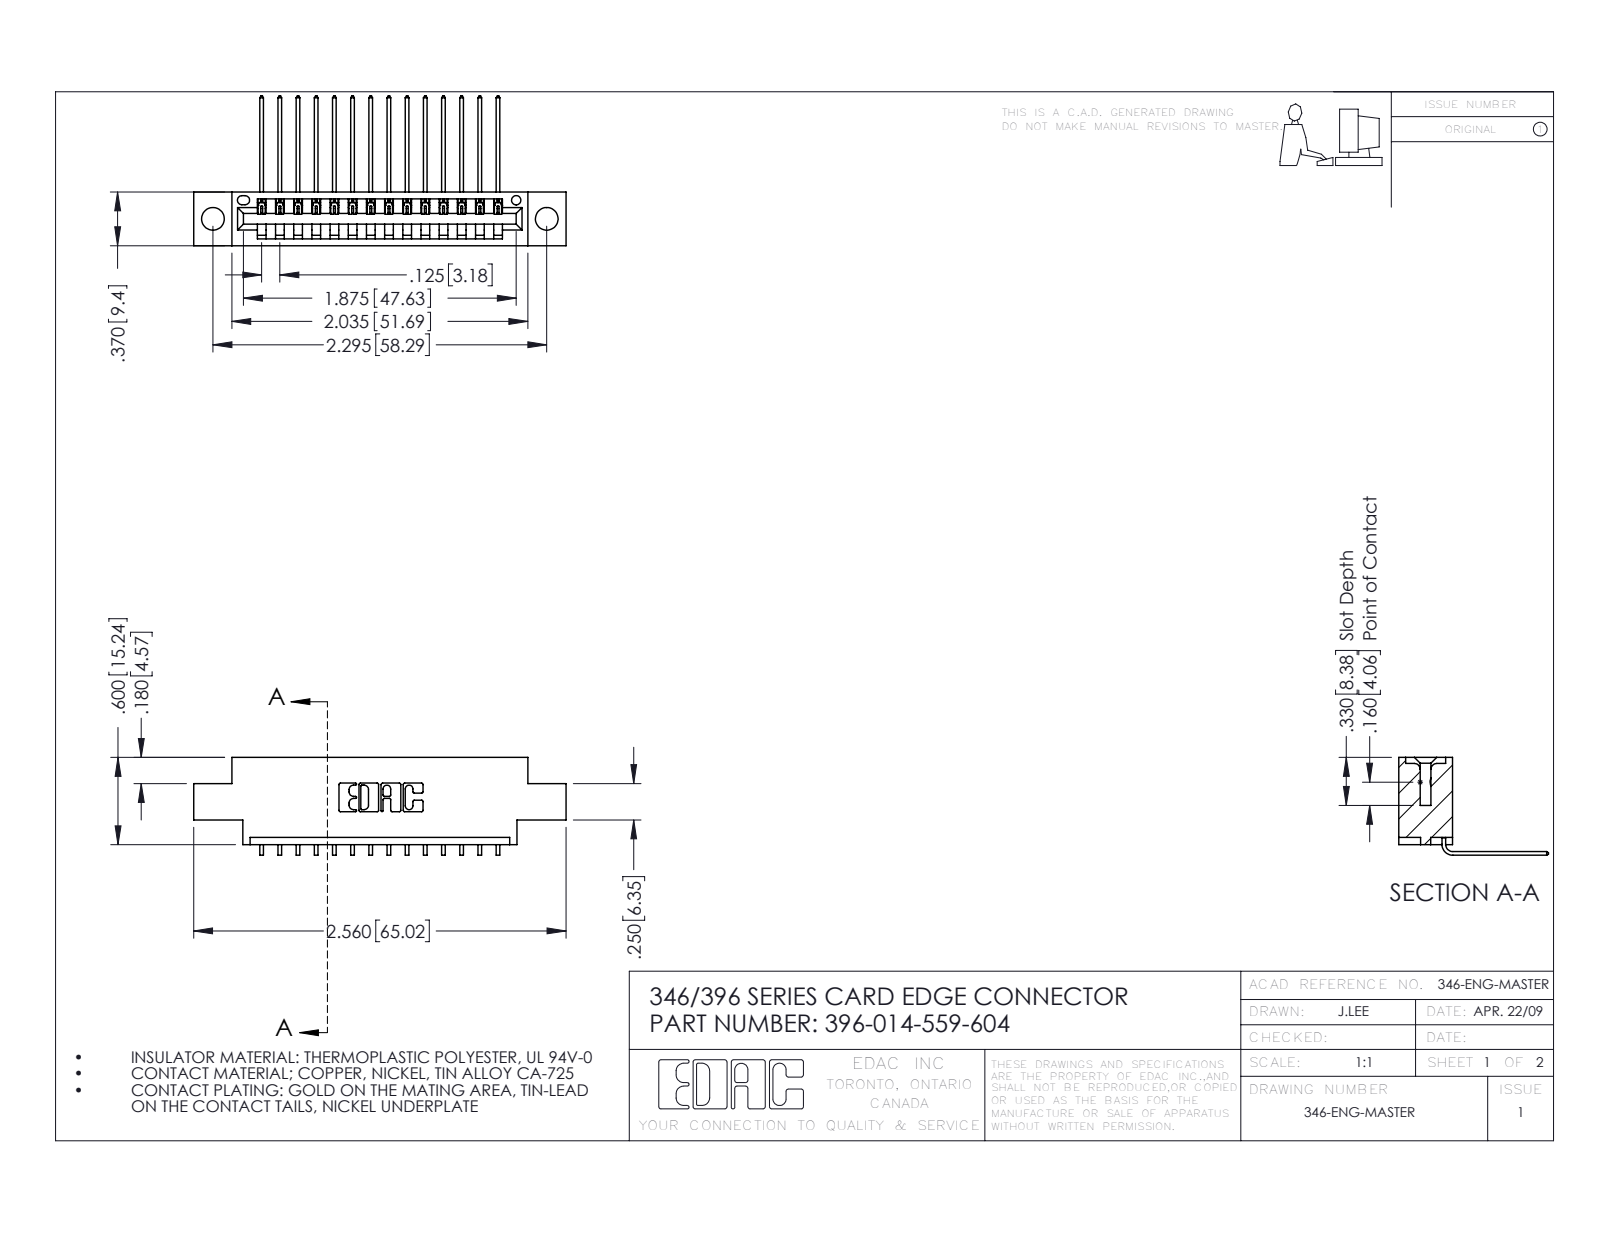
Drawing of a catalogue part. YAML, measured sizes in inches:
part_name: "346 Part_0.170 Offset - 0.156 Dia-TH; 345-292-001_558 559 Tail - 1; 396-014-559-604"
step_written_by: "SolidWorks 2016 (CONFIG_CONTROL_DESIGN)"
units: inches
bodies: {solids: 15, faces: 966, planar: 668, cylindrical: 298, other: 0}
overall_size: [2.56, 1.03, 0.673]
volume: 0.356
surface_area: 11.21
round_holes:
  - {diameter: 0.156, count: 2}
  - {diameter: 0.064, count: 1}
partial_cylinders:
  - {radius: 0.006, count: 28}
  - {radius: 0.01, count: 22}
  - {radius: 0.007, count: 6}
  - {radius: 0.031, count: 6}
  - {radius: 0.026, count: 3}
  - {radius: 0.031, count: 2}
  - {radius: 0.04, count: 2}
  - {radius: 0.014, count: 1}
face_to_face_distances: [0.048, 0.37, 0.322, 0.25, 0.025, 0.072, 0.148, 0.222, 0.1, 0.174]
hole_center_spacings: [0.246, 2.089, 2.295]
